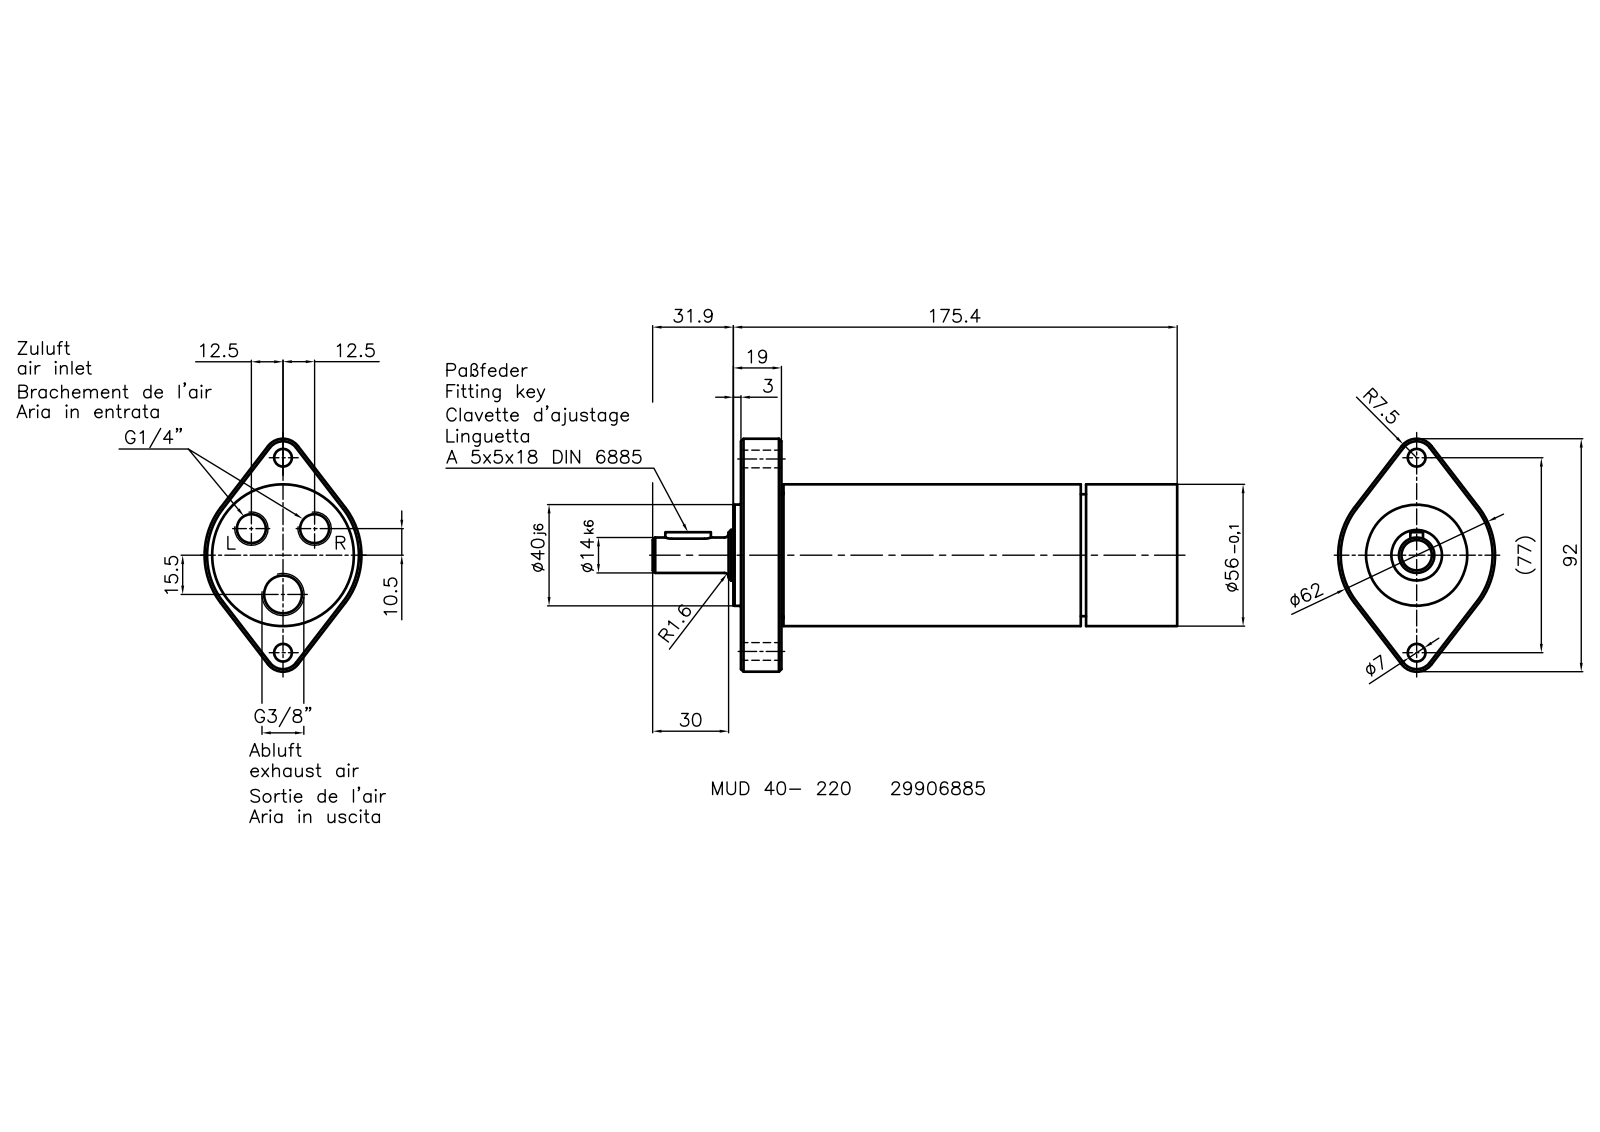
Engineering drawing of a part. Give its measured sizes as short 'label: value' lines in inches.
name: Bauteil1
written by: Autodesk Inventor 2008 (AUTOMOTIVE_DESIGN)
unit: in
bodies: 1 solid, 81 faces (30 planar, 14 cylindrical, 37 other)
size: 8.161 × 3.622 × 2.441
volume: 27.26 in³; area: 70.78 in²
holes: 1× ⌀0.837
bosses: 1× ⌀2.205, 1× ⌀1.89, 1× ⌀1.575, 1× ⌀0.787, 1× ⌀0.551
rounds: 2× R0.098, 2× R0.295, 1× R1.22
face distances: 6.787, 0.63, 6.157, 0.057, 4.683, 0.118, 0.748, 6.906, 0.805, 5.431
